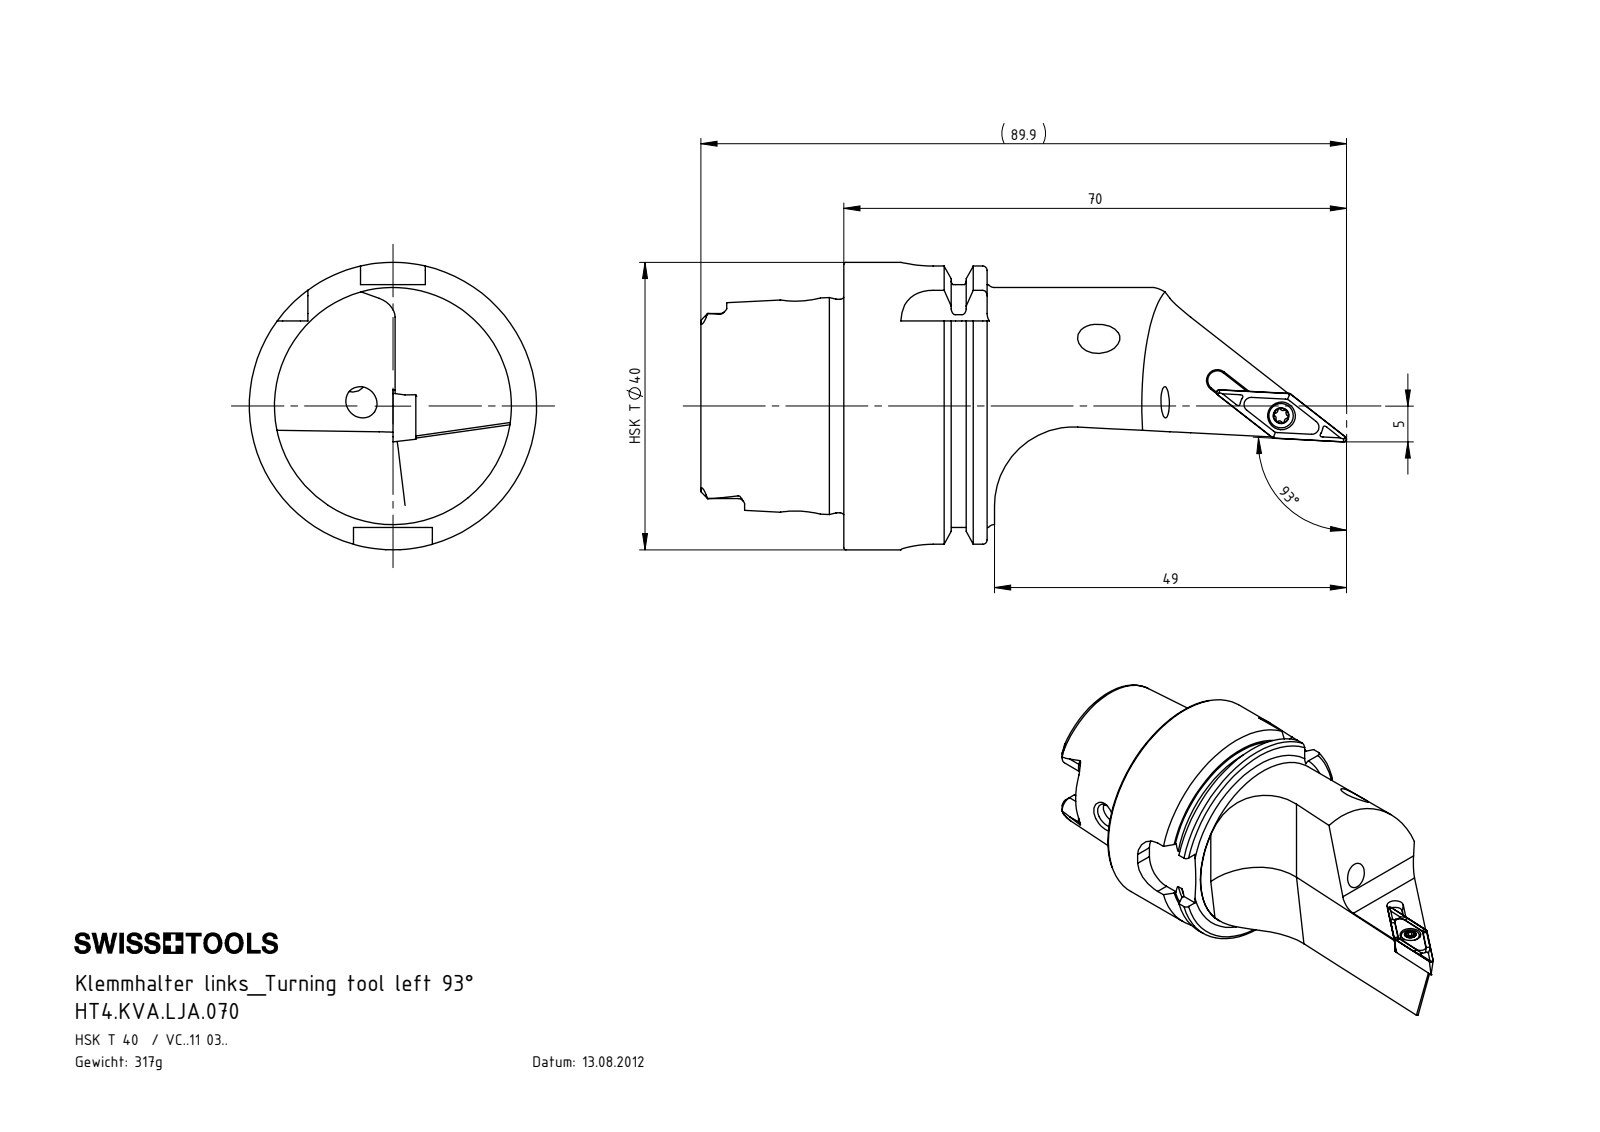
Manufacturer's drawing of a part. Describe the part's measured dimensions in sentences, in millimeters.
The part is named "WCA-ER2.001.006_A; WKX-ER1.004.005_A_PreviewCfg; HT4.KVA.LJA.070; HA4-KVA.LJA.070_B_Fertigbearbeitung (+2 more)". Its 3-D file was written by "SolidWorks 2022 (CONFIG_CONTROL_DESIGN)". It is 6 solids with 326 faces: 90 planar, 93 cylindrical and 143 other. Overall it measures 89.88 by 40 by 40 millimeters. Its volume is 40 295 cubic millimeters and its surface area 13 679 square millimeters. Round holes: 2 of diameter 4, 2 of diameter 4.2, 1 of diameter 1.7, 1 of diameter 2.05, 1 of diameter 2.8, 1 of diameter 3.3, 1 of diameter 3.85, 1 of diameter 4.6, 1 of diameter 5, 1 of diameter 10, 1 of diameter 11, 1 of diameter 12.5. Round bosses or shafts: 1 of diameter 40, 1 of diameter 34.75, 1 of diameter 33, 1 of diameter 29.71, 1 of diameter 5, 1 of diameter 4, 1 of diameter 3.4, 1 of diameter 2.5. Partial cylindrical surfaces (rounded edges, fillets, slot ends): 6 of radius 0.21, 6 of radius 0.9, 4 of radius 0.36, 4 of radius 1.88, 4 of radius 4.5, 2 of radius 0.36, 1 of radius 1.35, 1 of radius 3. The main face-to-face distances are 7.95, 19.95, 12, 19.9, 27.85, 39.85, 35.7, 15.8, 7.85, 4.15. The hole center spacings are 53.9, 53.96.
